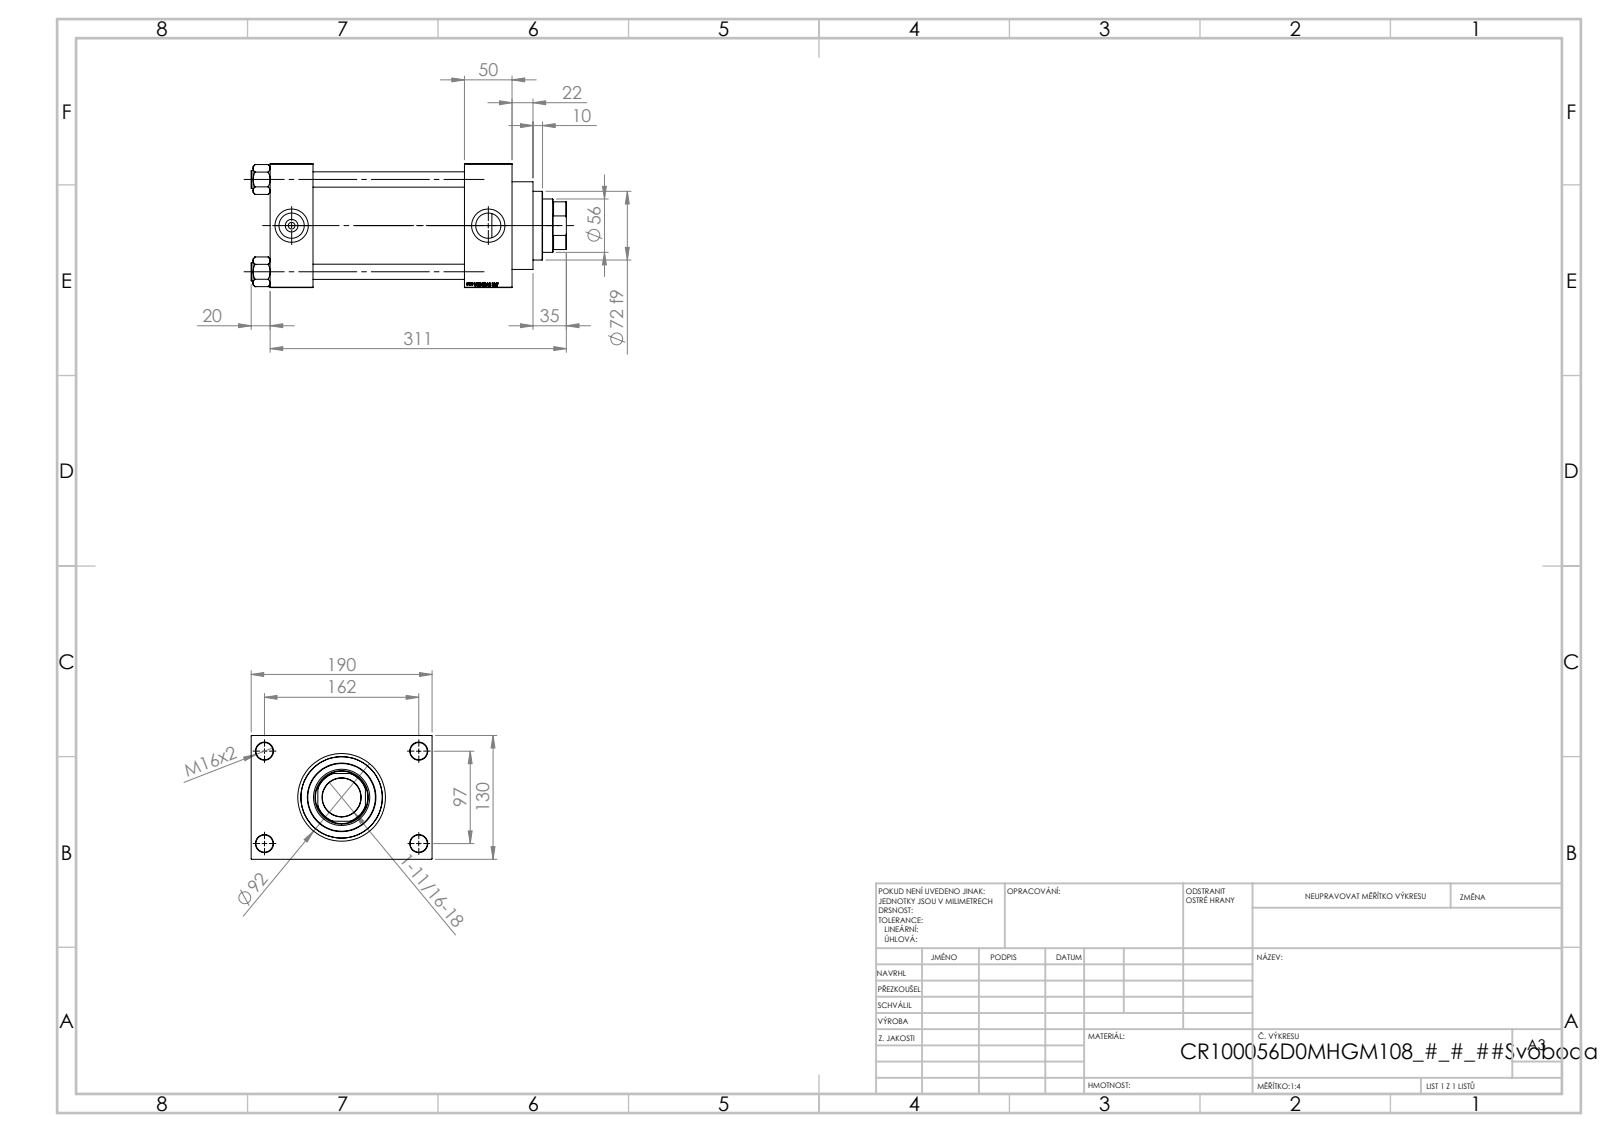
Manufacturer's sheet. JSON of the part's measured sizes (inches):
{"part_name": "NUT_M5_D; V215CR_D_Body; V215CR_D_TYCINKA; V215CR_VCP_D (+1 more)", "step_written_by": "SolidWorks 2019 (CONFIG_CONTROL_DESIGN)", "units": "inches", "bodies": {"solids": 11, "faces": 1151, "planar": 545, "cylindrical": 88, "other": 518}, "overall_size": [13.031, 7.48, 5.118], "volume_in3": 183.1, "surface_area_in2": 701.4, "round_holes": [[0.63, 4], [0.709, 4], [0.276, 2], [1.041, 2], [1.378, 2], [1.594, 1], [2.205, 1], [2.323, 1], [2.992, 1], [3.366, 1], [3.937, 1]], "round_bosses_or_shafts": [[0.748, 4], [4.173, 1], [3.622, 1], [2.835, 1]], "partial_cylinders_radius": [[1.063, 1]], "face_to_face_distances": [5.118, 1.969, 1.772, 8.031, 6.26, 10, 8.228, 1.181, 6.299, 7.48], "hole_center_spacings": [1.281, 2.698, 3.717, 3.815, 4.026, 5.096, 6.367, 3.819]}
